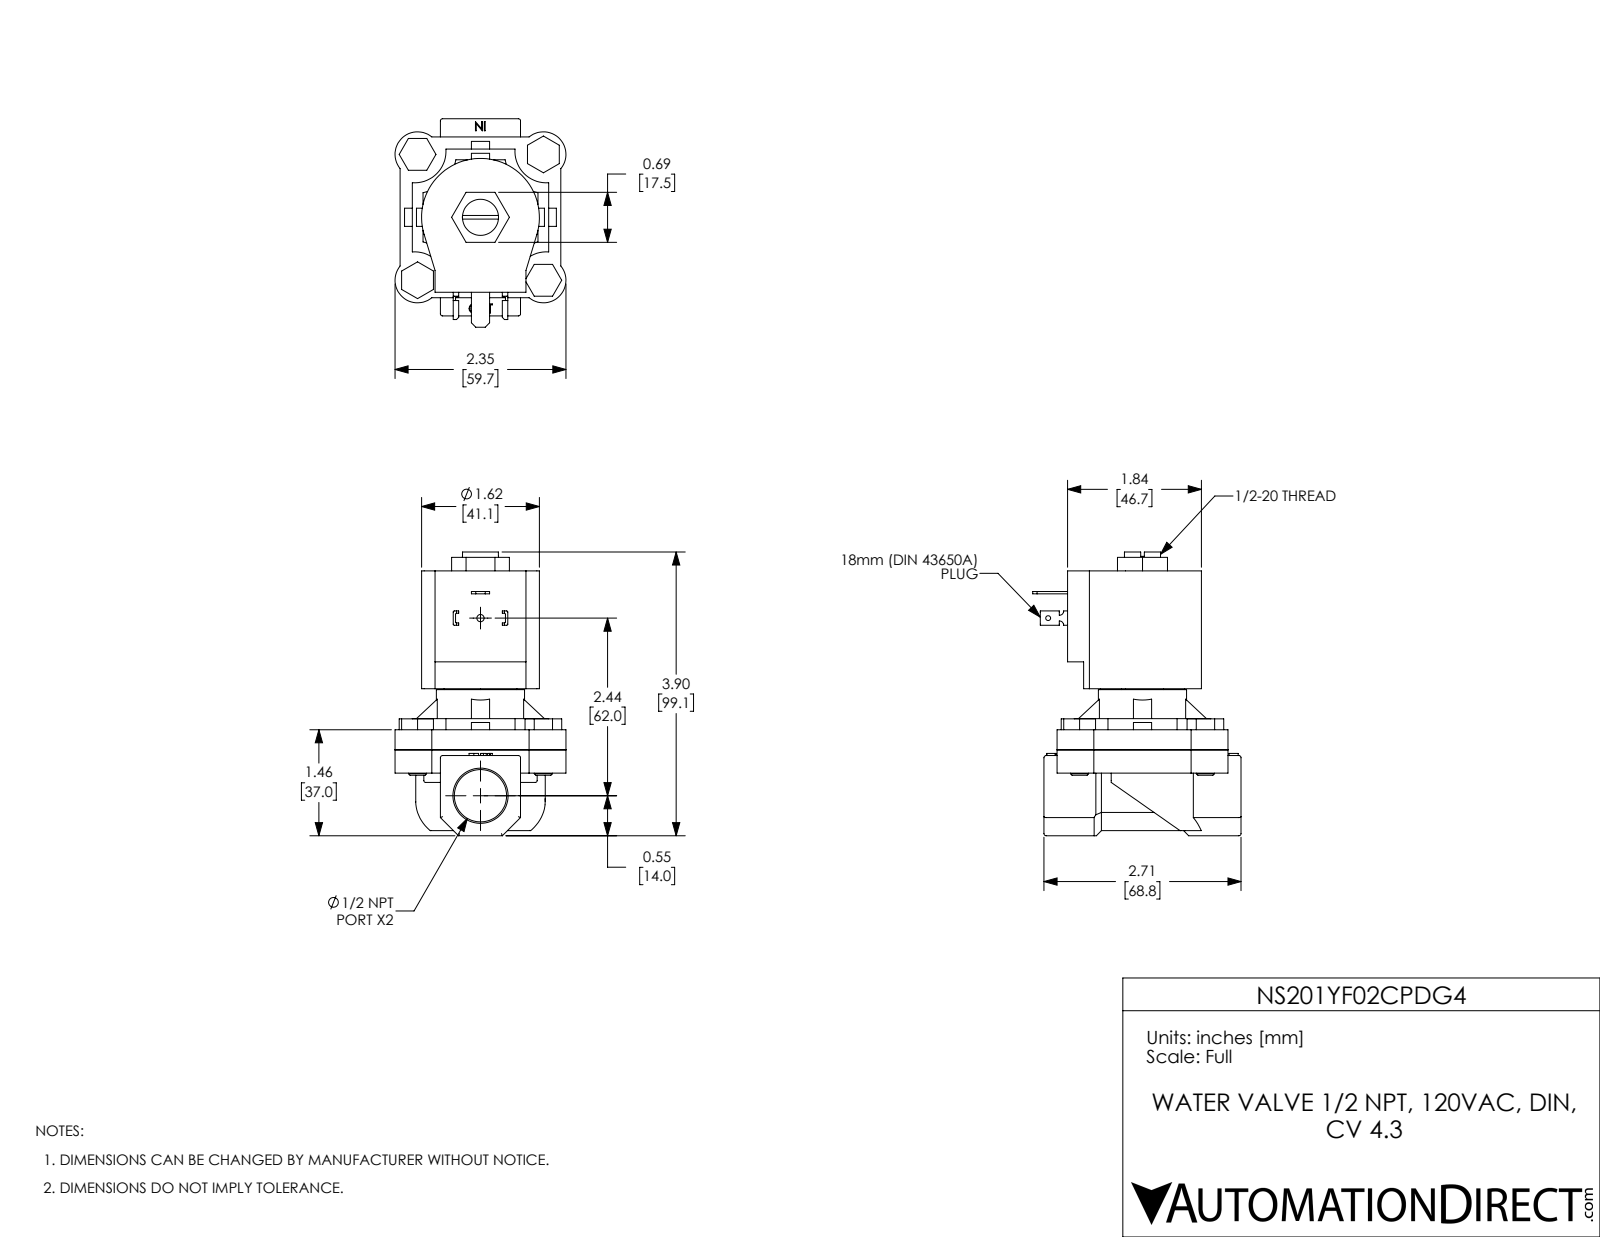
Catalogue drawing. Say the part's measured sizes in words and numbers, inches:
The part is named "NS201YF02CPDG4". Its 3-D file was written by "SolidWorks 2021 (CONFIG_CONTROL_DESIGN)". It is 11 solids with 385 faces: 239 planar, 113 cylindrical and 33 other. Overall it measures 3.9 by 2.865 by 2.35 inches. Its volume is 10.07 cubic inches and its surface area 67.48 square inches. Round holes: 4 of diameter 0.25, 1 of diameter 0.067, 1 of diameter 0.1, 1 of diameter 0.496, 1 of diameter 0.512, 1 of diameter 0.719, 1 of diameter 1.155. Round bosses or shafts: 4 of diameter 0.248, 1 of diameter 1.213. Partial cylindrical surfaces (rounded edges, fillets, slot ends): 15 of radius 0.03, 8 of radius 0.015, 4 of radius 0.31, 4 of radius 0.432, 4 of radius 0.579, 2 of radius 0.06, 1 of radius 0.81, 1 of radius 0.89. The main face-to-face distances are 0.276, 2.459, 2.183, 0.32, 0.596, 2.779, 0.554, 1.656, 0.25, 1.102. The hole center spacings are 1.223, 1.73, 2.446, 2.441.
